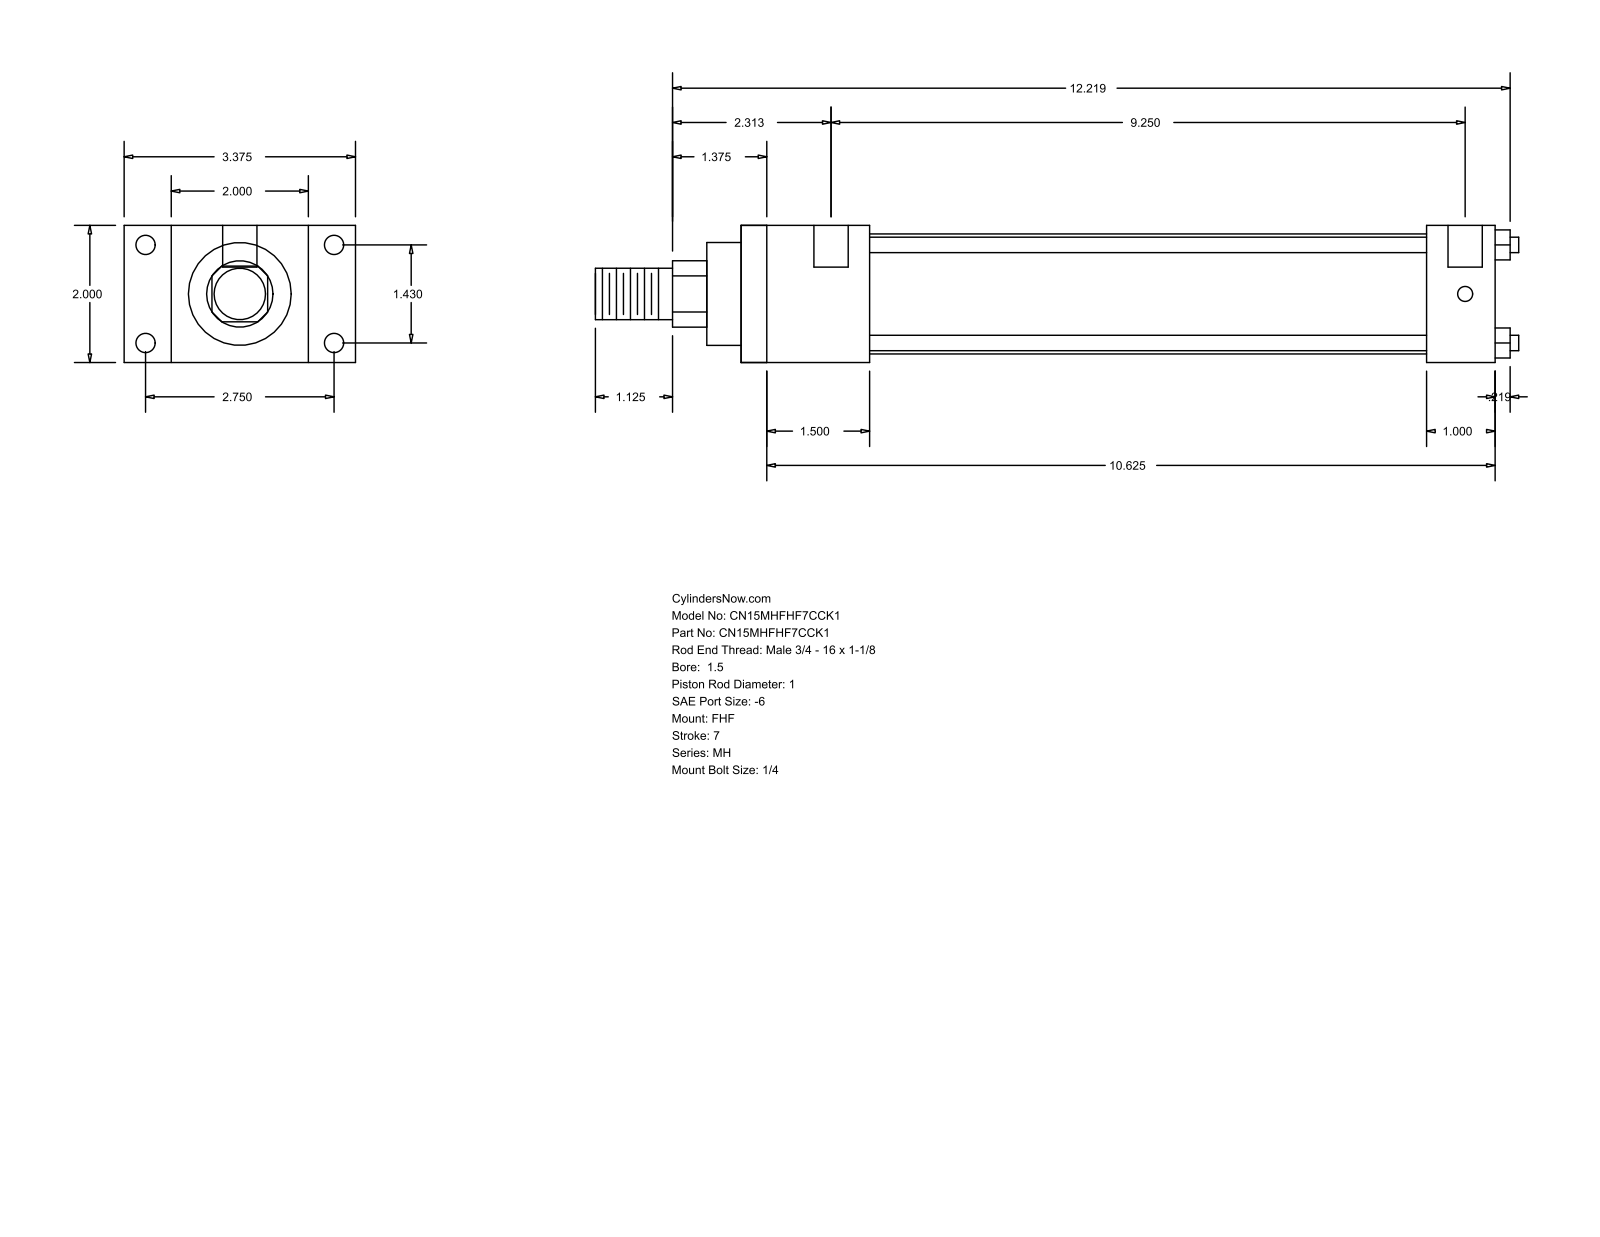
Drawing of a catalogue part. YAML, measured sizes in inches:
part_name: "MH_FHF__0150_1"
step_written_by: "GSSL Pune (CONFIG_CONTROL_DESIGN)"
units: inches
bodies: {solids: 0, faces: 88, planar: 60, cylindrical: 28, other: 0}
overall_size: [13.469, 3.375, 2]
round_holes:
  - {diameter: 0.219, count: 4}
  - {diameter: 0.281, count: 4}
  - {diameter: 0.5, count: 2}
round_bosses_or_shafts:
  - {diameter: 0.225, count: 4}
  - {diameter: 1.75, count: 1}
  - {diameter: 1.5, count: 1}
  - {diameter: 1, count: 1}
  - {diameter: 0.75, count: 1}
partial_cylinders:
  - {radius: 0.484, count: 1}
face_to_face_distances: [2, 0.687, 2.687, 1.875, 3.375, 11, 9.125, 1, 10, 8.125]
hole_center_spacings: [1.43, 2.75, 3.099, 9.375, 0.125, 9.25]
